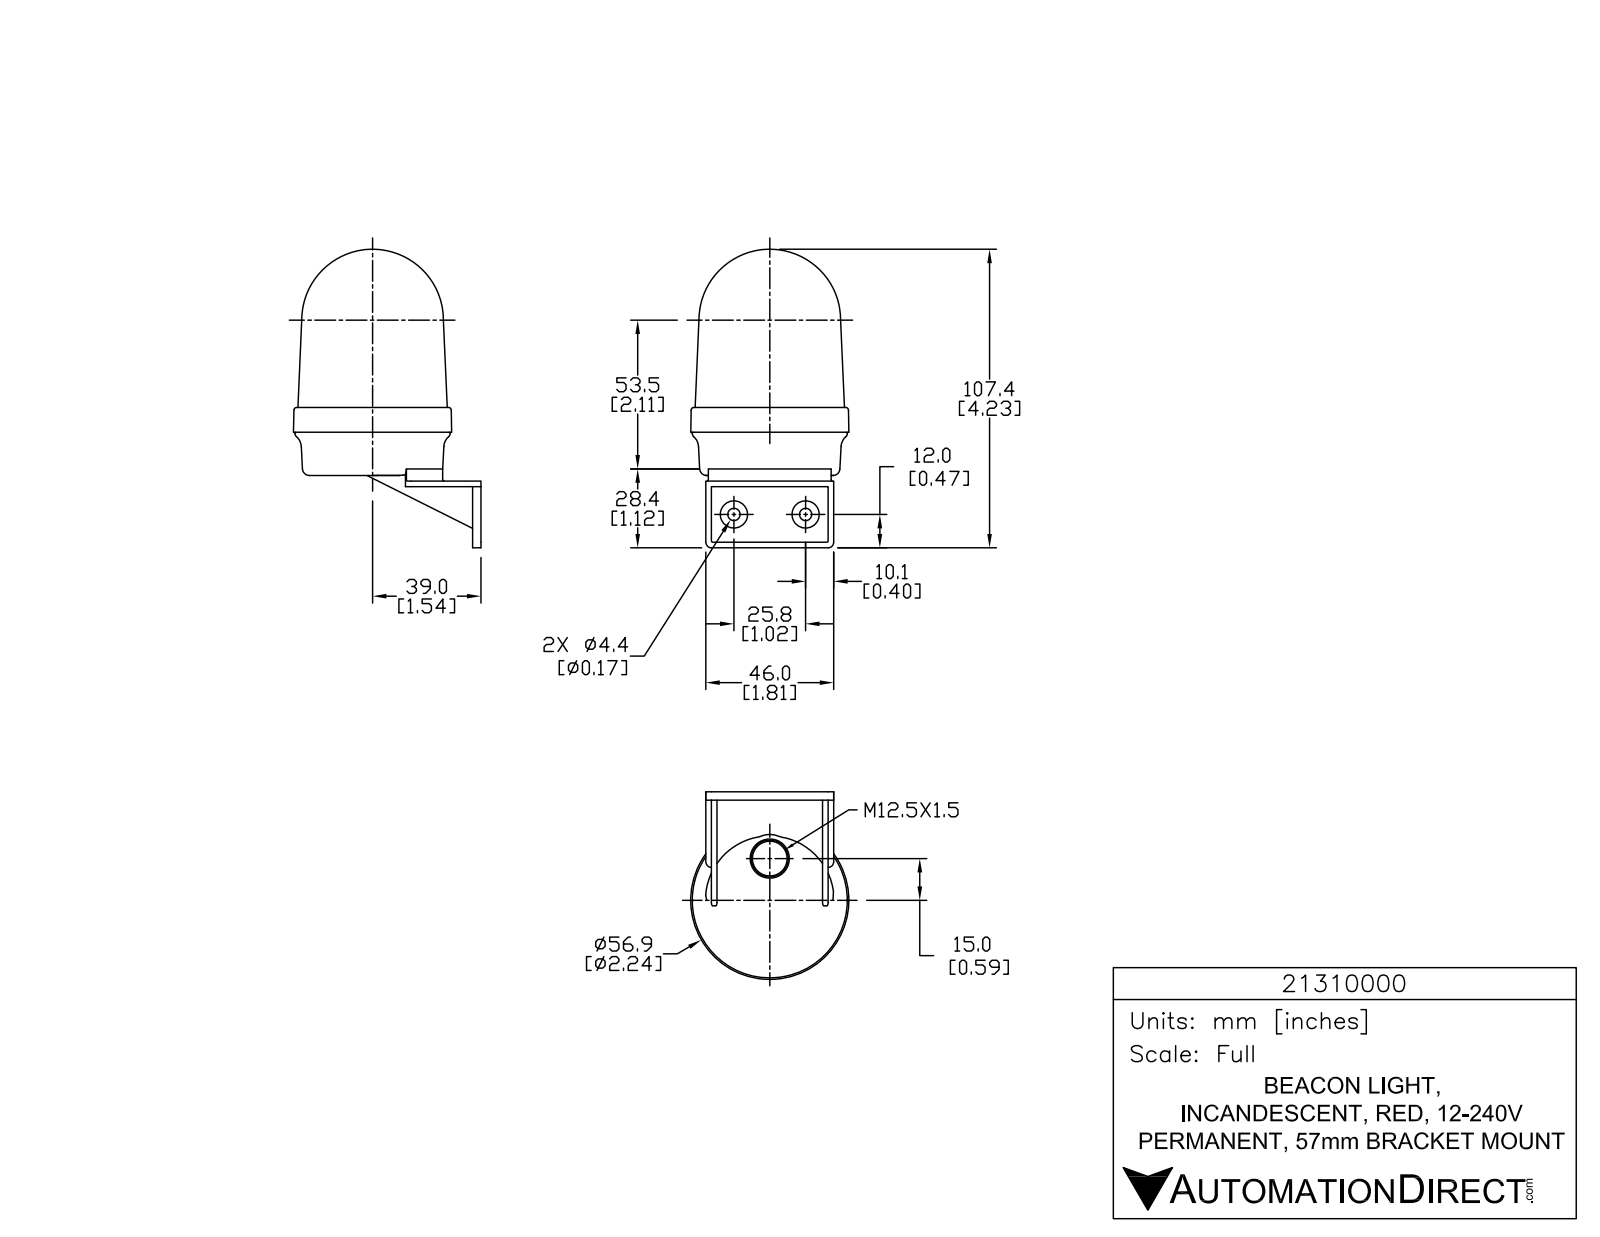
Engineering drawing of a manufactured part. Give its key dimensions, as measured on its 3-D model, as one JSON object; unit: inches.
{"part_name": "21310000", "step_written_by": "SolidWorks 2015 (AUTOMOTIVE_DESIGN)", "units": "inches", "bodies": {"solids": 1, "faces": 826, "planar": 550, "cylindrical": 178, "other": 98}, "overall_size": [4.228, 2.838, 2.392], "volume_in3": 9.936, "surface_area_in2": 32.97, "round_holes": [[0.039, 3], [0.173, 2]], "round_bosses_or_shafts": [[0.226, 3], [0.056, 3], [0.386, 2], [2.197, 1]], "partial_cylinders_radius": [[0.008, 6], [0.008, 6], [0.008, 6], [0.02, 6], [0.131, 6], [0.079, 4], [0.004, 3], [0.005, 3]], "face_to_face_distances": [0.079, 0.157, 1.575, 1.654, 0.039, 0.118, 1.496, 0.866, 0.945, 0.772], "hole_center_spacings": [1.016]}
